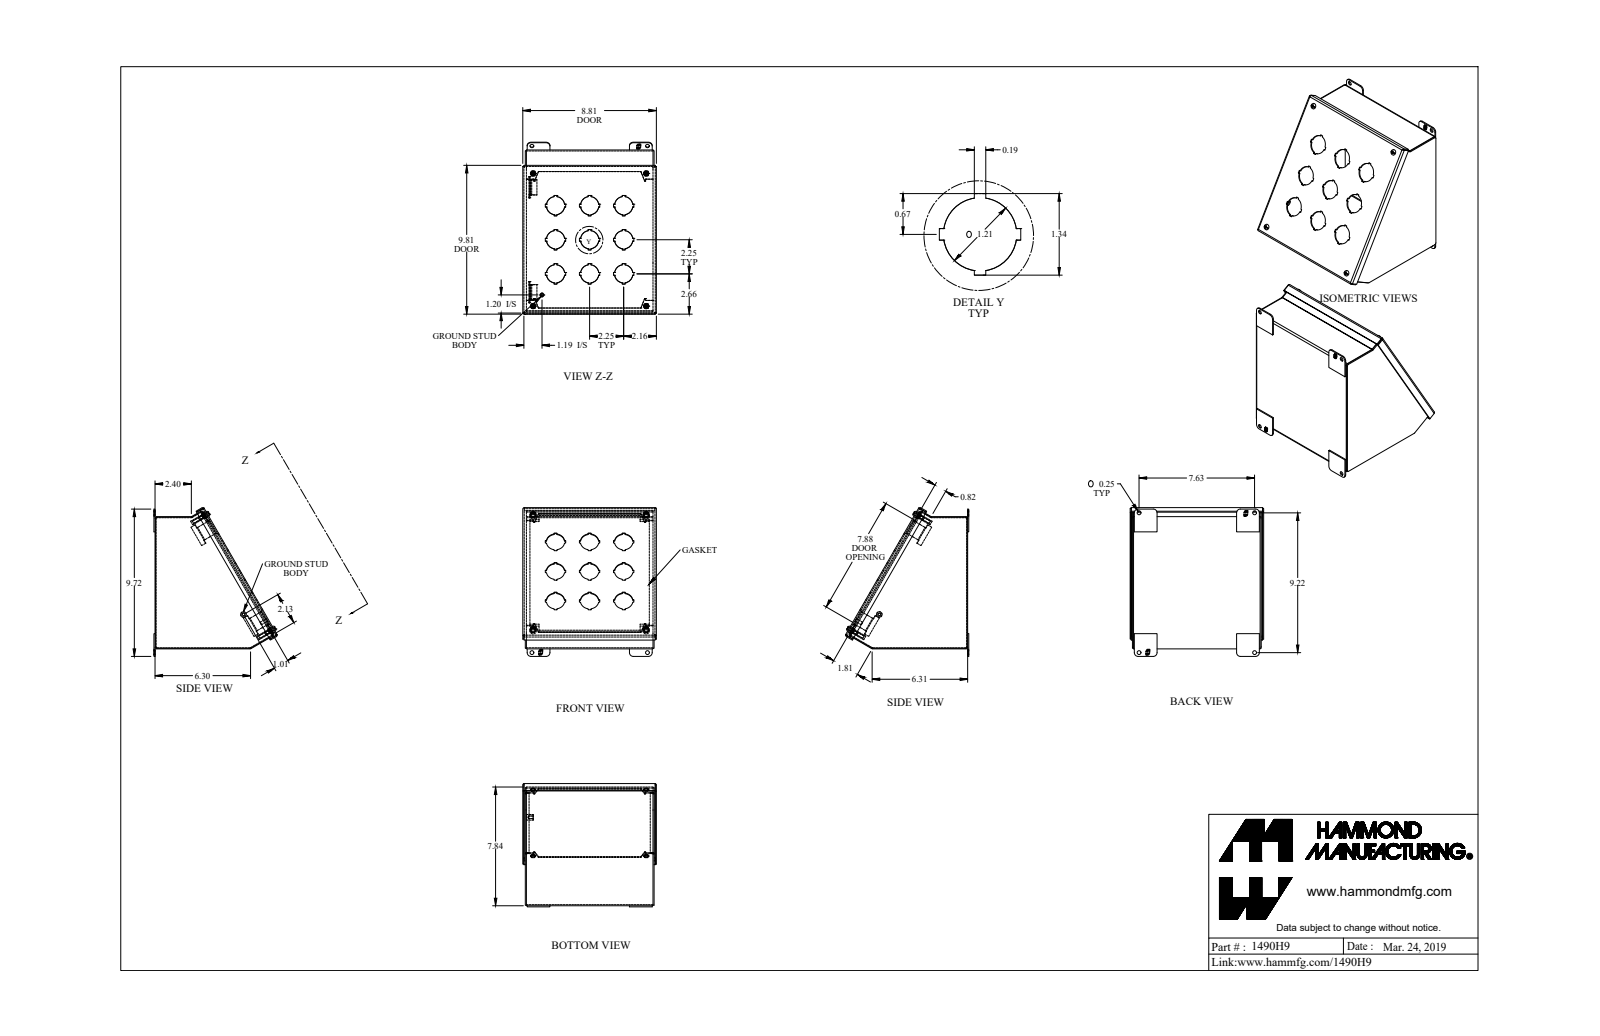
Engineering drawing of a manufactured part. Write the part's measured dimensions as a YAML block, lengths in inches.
part_name: "1490H9_Default"
step_written_by: "SolidWorks 2019 (CONFIG_CONTROL_DESIGN)"
units: inches
bodies: {solids: 25, faces: 855, planar: 607, cylindrical: 208, other: 40}
overall_size: [9.818, 8.812, 8.133]
volume: 30.77
surface_area: 827.5
round_holes:
  - {diameter: 1.21, count: 9}
  - {diameter: 0.25, count: 8}
  - {diameter: 0.159, count: 4}
  - {diameter: 0.406, count: 4}
  - {diameter: 0.156, count: 1}
round_bosses_or_shafts:
  - {diameter: 0.39, count: 4}
  - {diameter: 0.275, count: 4}
  - {diameter: 0.19, count: 4}
  - {diameter: 0.148, count: 4}
  - {diameter: 0.375, count: 1}
  - {diameter: 0.25, count: 1}
  - {diameter: 0.188, count: 1}
partial_cylinders:
  - {radius: 0.108, count: 18}
  - {radius: 0.036, count: 12}
  - {radius: 0.029, count: 8}
  - {radius: 0.086, count: 8}
  - {radius: 0.25, count: 8}
  - {radius: 0.125, count: 4}
  - {radius: 0.16, count: 4}
  - {radius: 0.171, count: 4}
face_to_face_distances: [0.072, 8.428, 8.356, 8.5, 8.646, 8.718, 8.574, 0.25, 0.322, 9.428]
hole_center_spacings: [7.46, 8.75, 2.25, 3.182, 5.031, 2.59, 6.788, 7.474]
